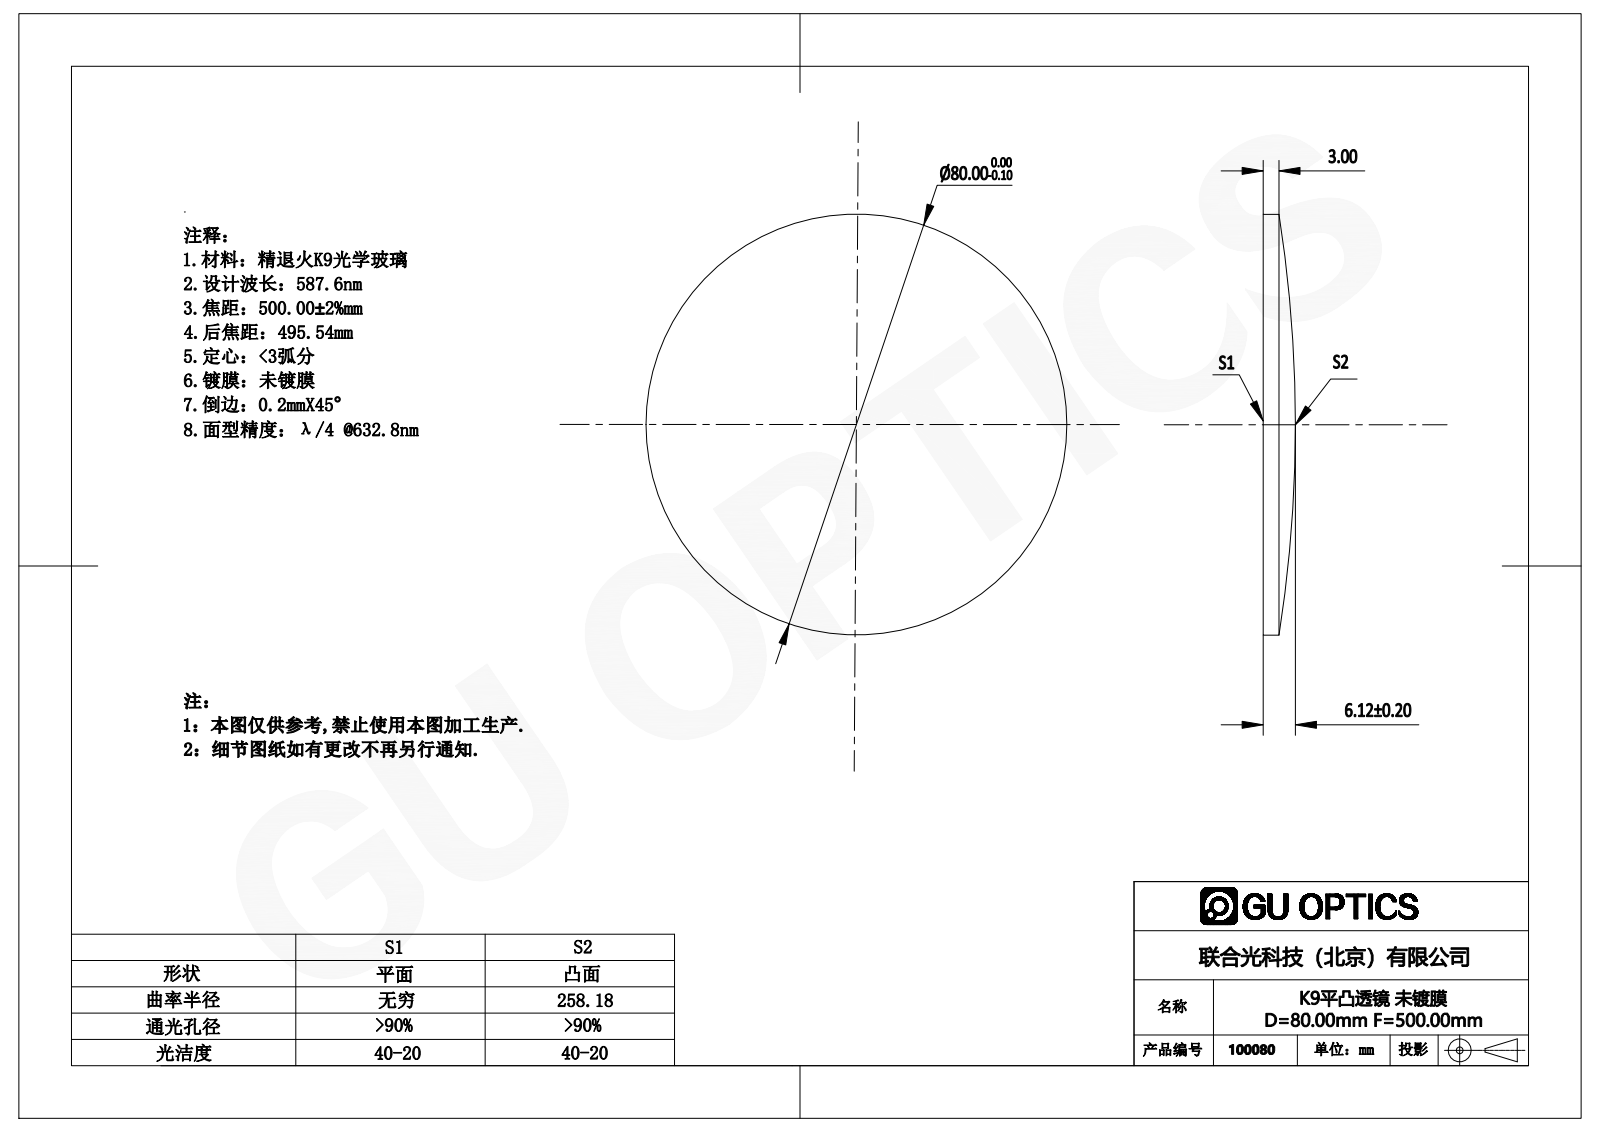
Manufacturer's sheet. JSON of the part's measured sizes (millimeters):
{"part_name": "100080", "step_written_by": "SolidWorks 2016 (AUTOMOTIVE_DESIGN)", "units": "millimeters", "bodies": {"solids": 1, "faces": 5, "planar": 1, "cylindrical": 2, "other": 2}, "overall_size": [80, 80, 6.12], "volume_mm3": 22937, "surface_area_mm2": 10838, "round_bosses_or_shafts": [[80, 1]]}
